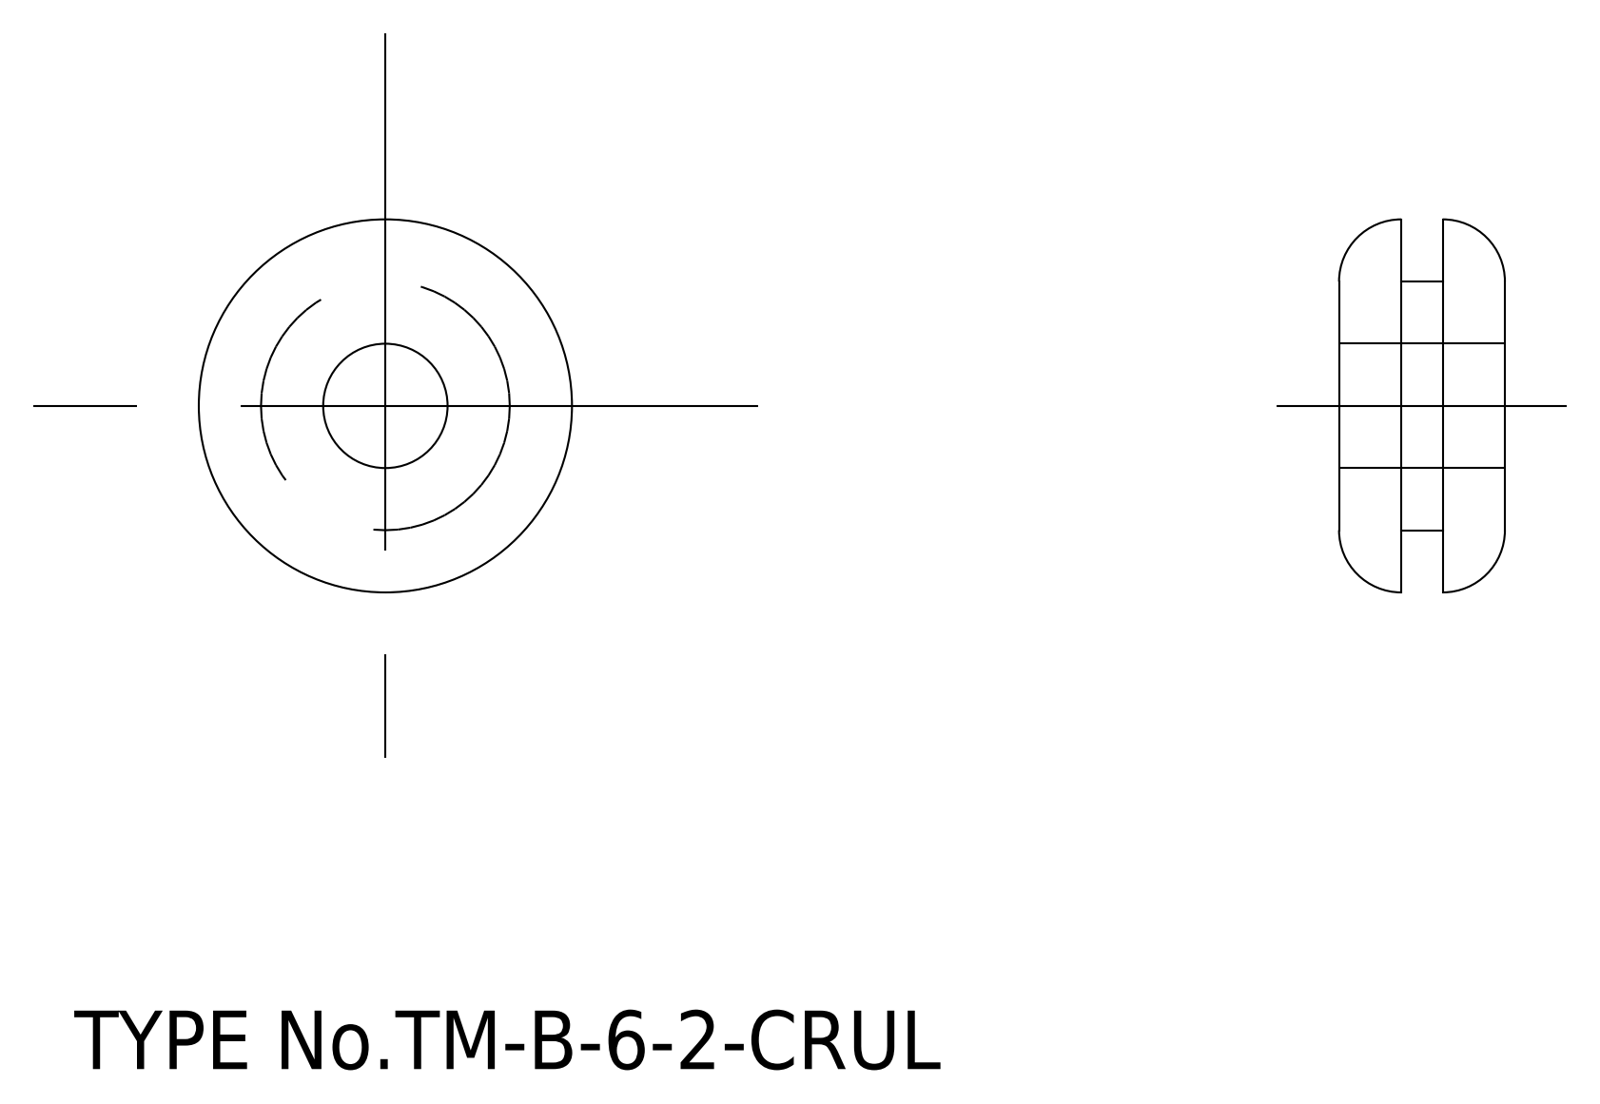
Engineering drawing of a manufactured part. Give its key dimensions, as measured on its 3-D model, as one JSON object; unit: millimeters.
{"step_written_by": "spGate 15.6.1 (AUTOMOTIVE_DESIGN)", "units": "millimeters", "bodies": {"solids": 1, "faces": 12, "planar": 4, "cylindrical": 4, "other": 4}, "overall_size": [18, 18, 8], "volume_mm3": 1325, "surface_area_mm2": 1147, "round_holes": [[6, 1]], "round_bosses_or_shafts": [[12, 1]], "face_to_face_distances": [3, 5, 2, 8]}
